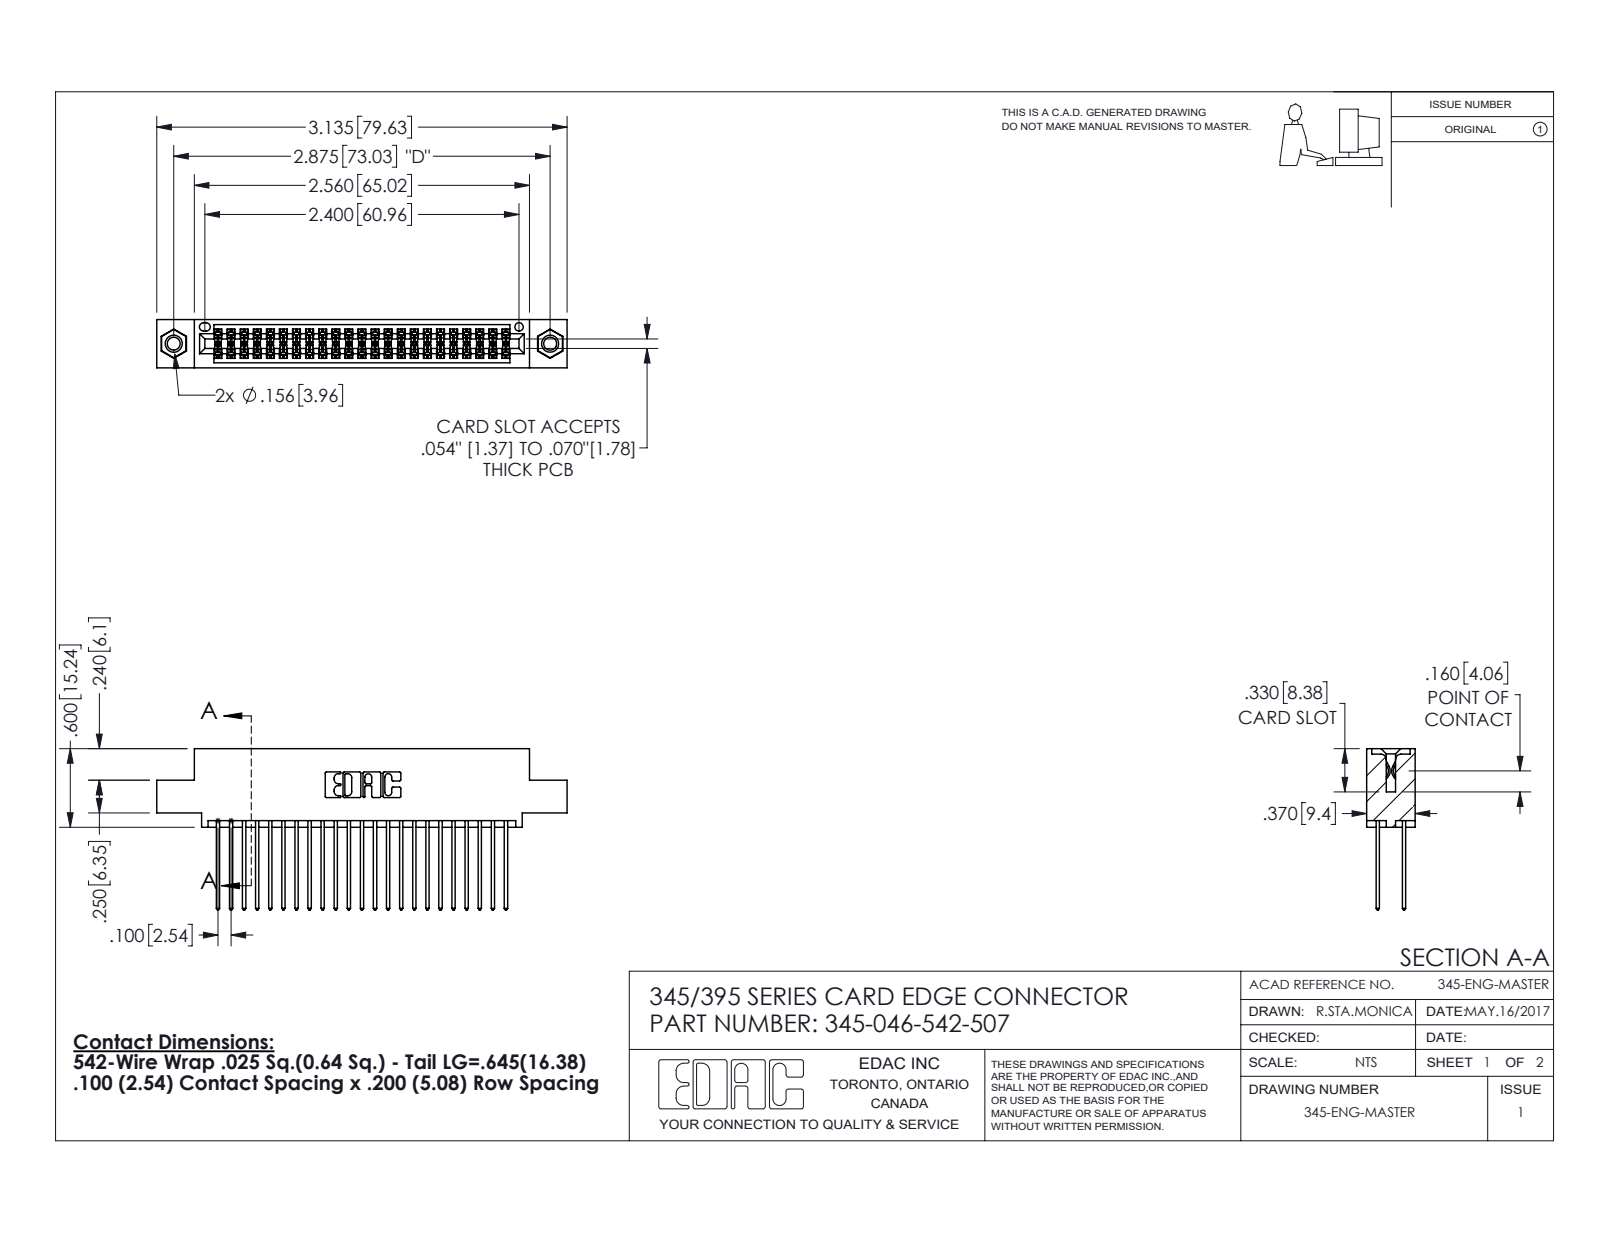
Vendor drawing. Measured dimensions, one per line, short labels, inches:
name: 345 Part_0.110 Offset - 0.156 Dia-TI; 345-250-001_345-250-005-103; 345-046-542-507; 345-292-001_345-293-142
written by: SolidWorks 2016 (CONFIG_CONTROL_DESIGN)
unit: in
bodies: 49 solids, 2490 faces (1634 planar, 840 cylindrical, 16 other)
size: 3.135 × 1.232 × 0.37
volume: 0.469 in³; area: 18.78 in²
holes: 2× ⌀0.098, 2× ⌀0.125, 2× ⌀0.156, 1× ⌀0.064
bosses: 2× ⌀0.155
rounds: 69× R0.006, 46× R0.01, 22× R0.01, 6× R0.007, 6× R0.031, 3× R0.026, 2× R0.014, 2× R0.019
face distances: 0.072, 0.298, 0.2, 0.098, 0.272, 0.025, 0.37, 0.225, 0.175, 0.149
hole spacings: 0.27, 2.641, 2.875
